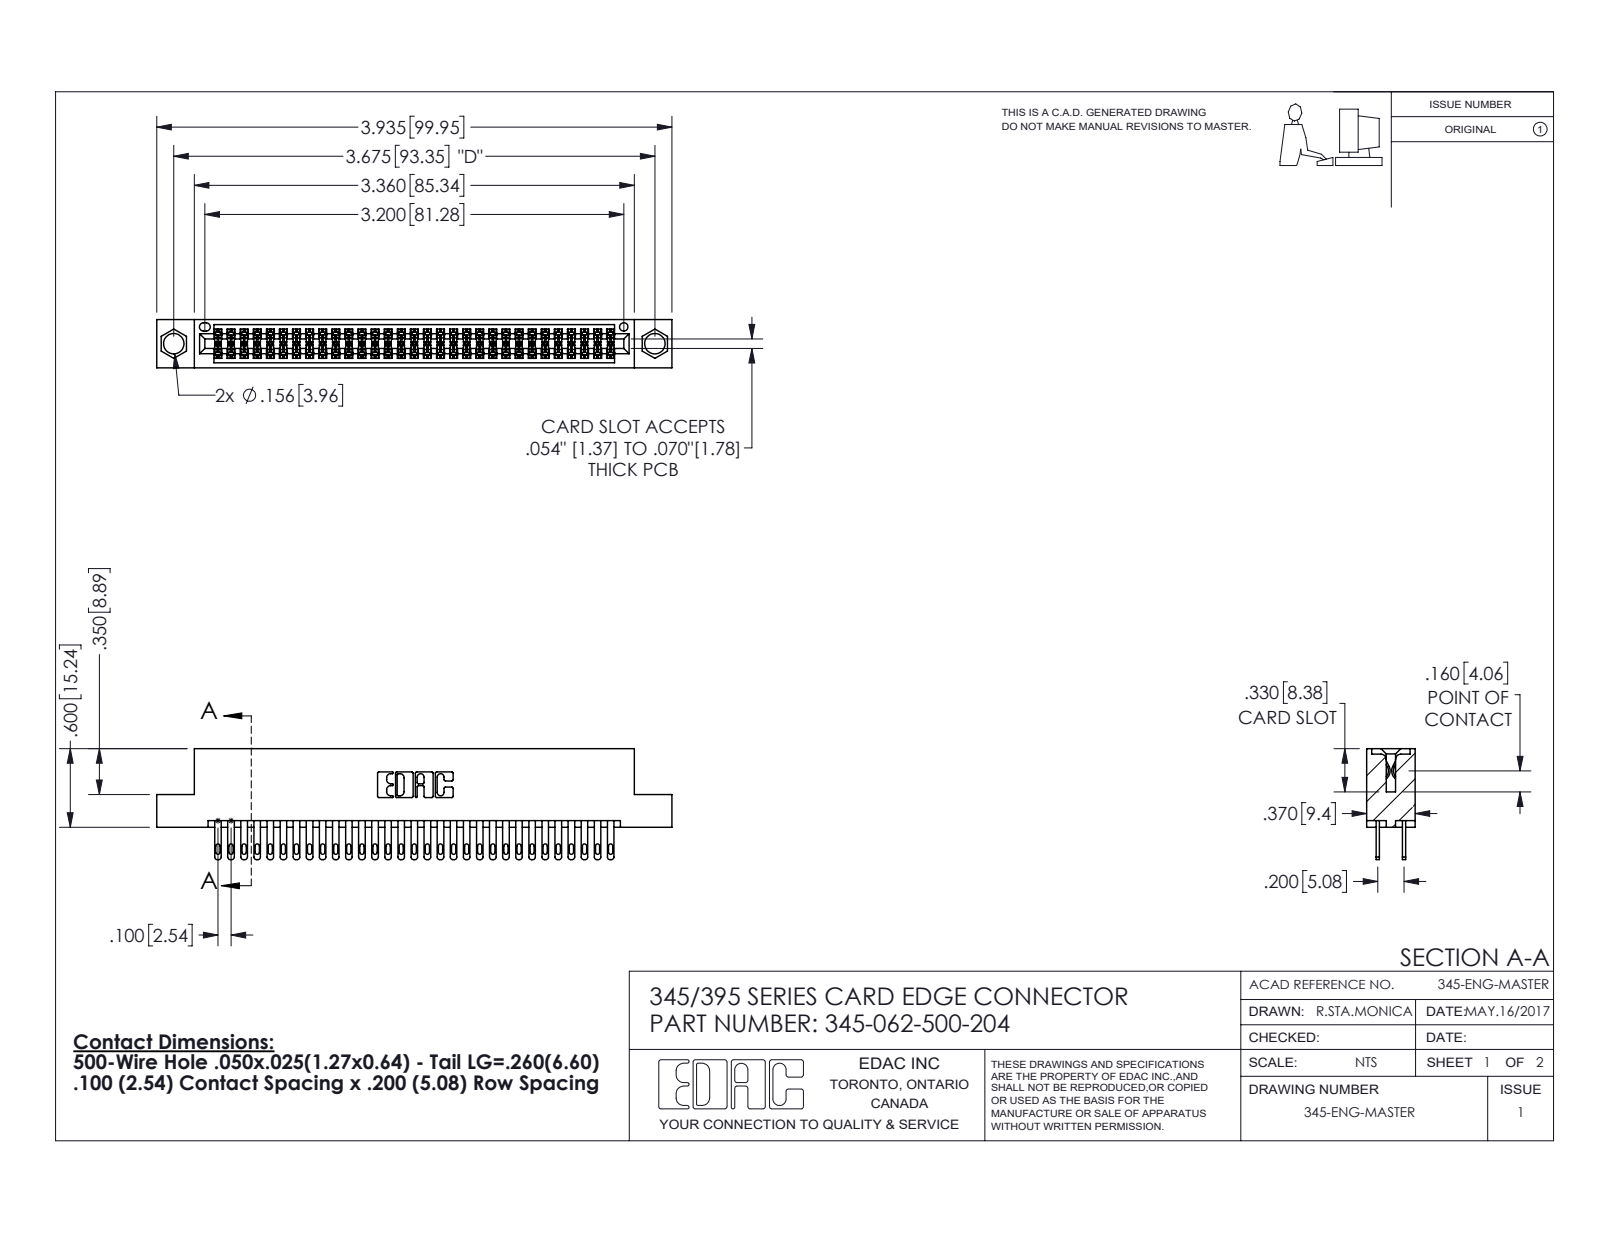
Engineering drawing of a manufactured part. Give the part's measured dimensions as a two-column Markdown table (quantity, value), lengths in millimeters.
| quantity | value |
| --- | --- |
| part name | 345 Part_Flush Mounting Lugs - 0.156 Dia-TI; 345-292-001_345-293-100; 345-062-500-204 |
| STEP written by | SolidWorks 2020 (CONFIG_CONTROL_DESIGN) |
| units | millimeters |
| bodies | 63 solids, 2992 faces (1768 planar, 1224 cylindrical, 0 other) |
| overall size | 99.9 × 21.5 × 9.4 |
| volume | 9 680 mm³ |
| surface area | 14 590 mm² |
| round holes (diameter × count) | 4 × 2, 1.6 × 1 |
| partial cylindrical surfaces (radius × count) | 0.2 × 93, 0.4 × 62, 0.5 × 62, 0.3 × 22, 0.2 × 6, 0.8 × 6, 0.7 × 3, 0.4 × 2 |
| main face-to-face distances | 7.6, 1.8, 5.1, 2.5, 6.9, 0.6, 9.4, 5.7, 4.4, 3.8 |
| hole center spacings | 6.9, 87.4, 93.3 |
